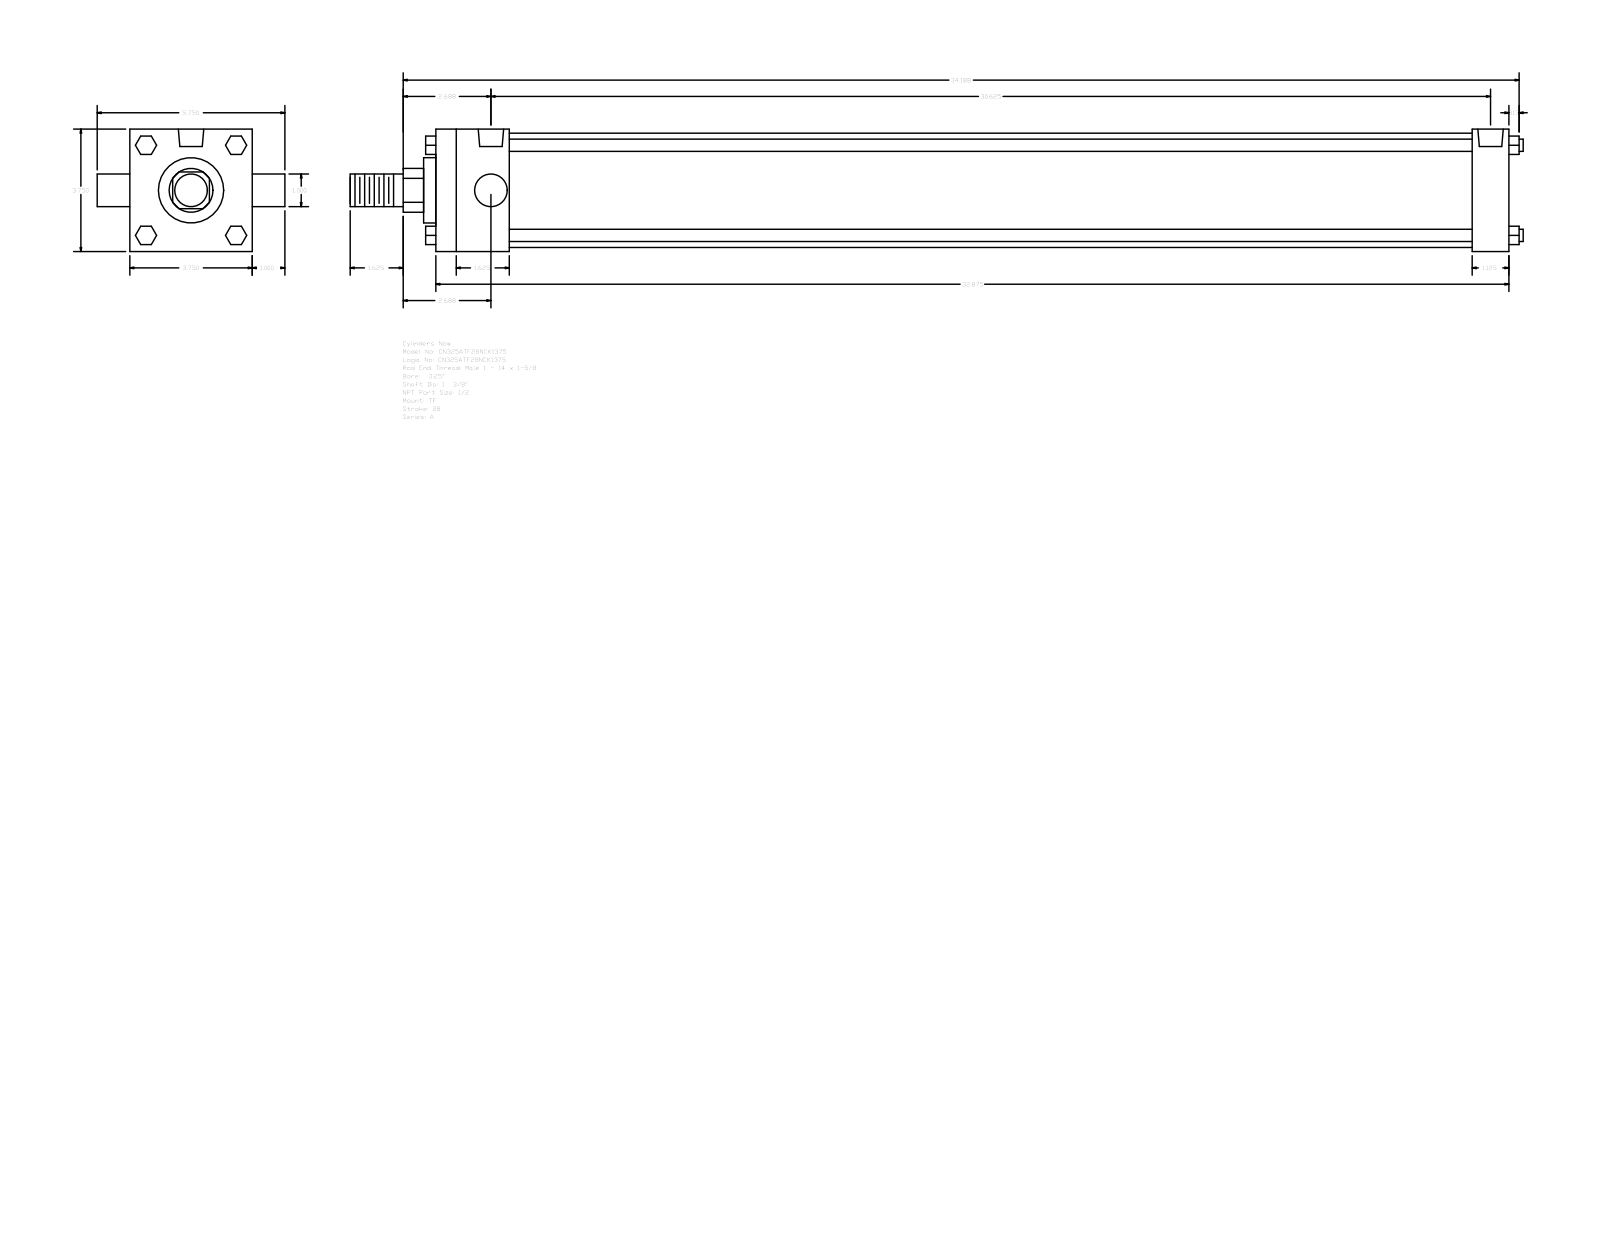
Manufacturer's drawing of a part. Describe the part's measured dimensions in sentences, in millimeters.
The part is named "A_TF__0325_1.375". Its 3-D file was written by "GSSL Pune (CONFIG_CONTROL_DESIGN)". It is 0 solids with 120 faces: 92 planar, 28 cylindrical and 0 other. Overall it measures 912.81 by 146.05 by 95.25 millimeters. Round holes: 3 of diameter 8.73, 2 of diameter 19.77. Round bosses or shafts: 4 of diameter 9.53, 2 of diameter 25.4, 1 of diameter 88.9, 1 of diameter 50.8, 1 of diameter 34.92. Partial cylindrical surfaces (rounded edges, fillets, slot ends): 1 of radius 17.06. The main face-to-face distances are 95.24, 835.02, 57.15, 806.45, 749.3, 777.87, 28.57, 66.67, 9.52, 815.97. The hole center spacings are 3.18, 774.7, 771.52, 777.88.
